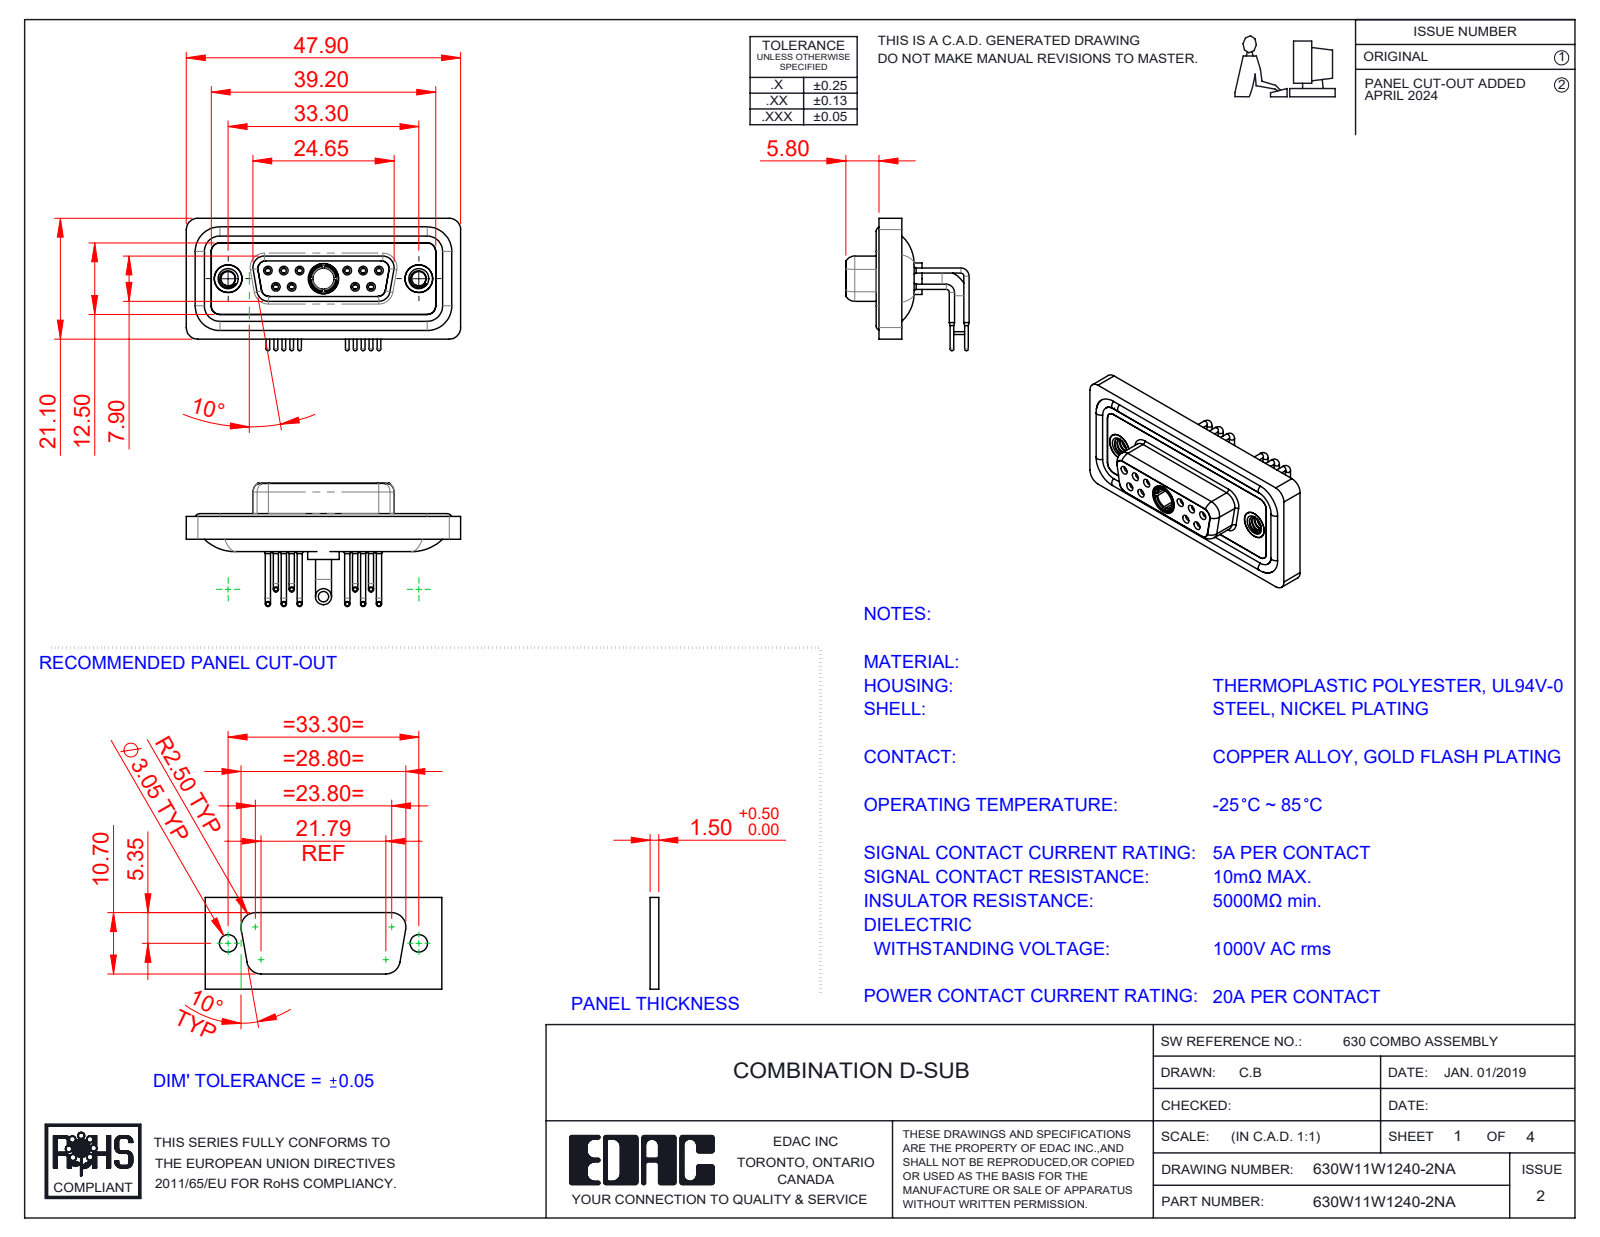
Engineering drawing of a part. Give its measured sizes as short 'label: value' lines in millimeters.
name: 630Combo Housing_11W1; 630Combo Waterproof Housing_15 Contacts; 630W11W1140-2NA; 630Combo Contact Row 1_50 Contacts (+5 more)
written by: SolidWorks 2020 (CONFIG_CONTROL_DESIGN)
unit: mm
bodies: 19 solids, 988 faces (284 planar, 441 cylindrical, 263 other)
size: 47.9 × 23.12 × 21.53
volume: 6 210 mm³; area: 10 474 mm²
holes: 10× ⌀0.9, 10× ⌀1.1, 10× ⌀1.5, 10× ⌀2, 6× ⌀1.7, 4× ⌀1.6, 3× ⌀4.85, 2× ⌀2.5, 2× ⌀4, 2× ⌀4.05, 2× ⌀5, 1× ⌀3.7
bosses: 10× ⌀1.6, 10× ⌀0.9, 10× ⌀0.65, 2× ⌀4.95, 2× ⌀4.8, 2× ⌀2.8, 1× ⌀5.5, 1× ⌀5.2
rounds: 20× R2, 18× R1.5, 12× R1.35, 8× R1.6, 4× R0.25, 4× R0.5, 4× R0.6, 4× R0.65
face distances: 0.4, 1.8, 1.1, 1.6, 2.5, 2.9, 3.1, 3.7, 4.1, 1.5
hole spacings: 3.16, 2.77, 13.85, 11.08, 16.62, 5.03, 5.04, 5.54
